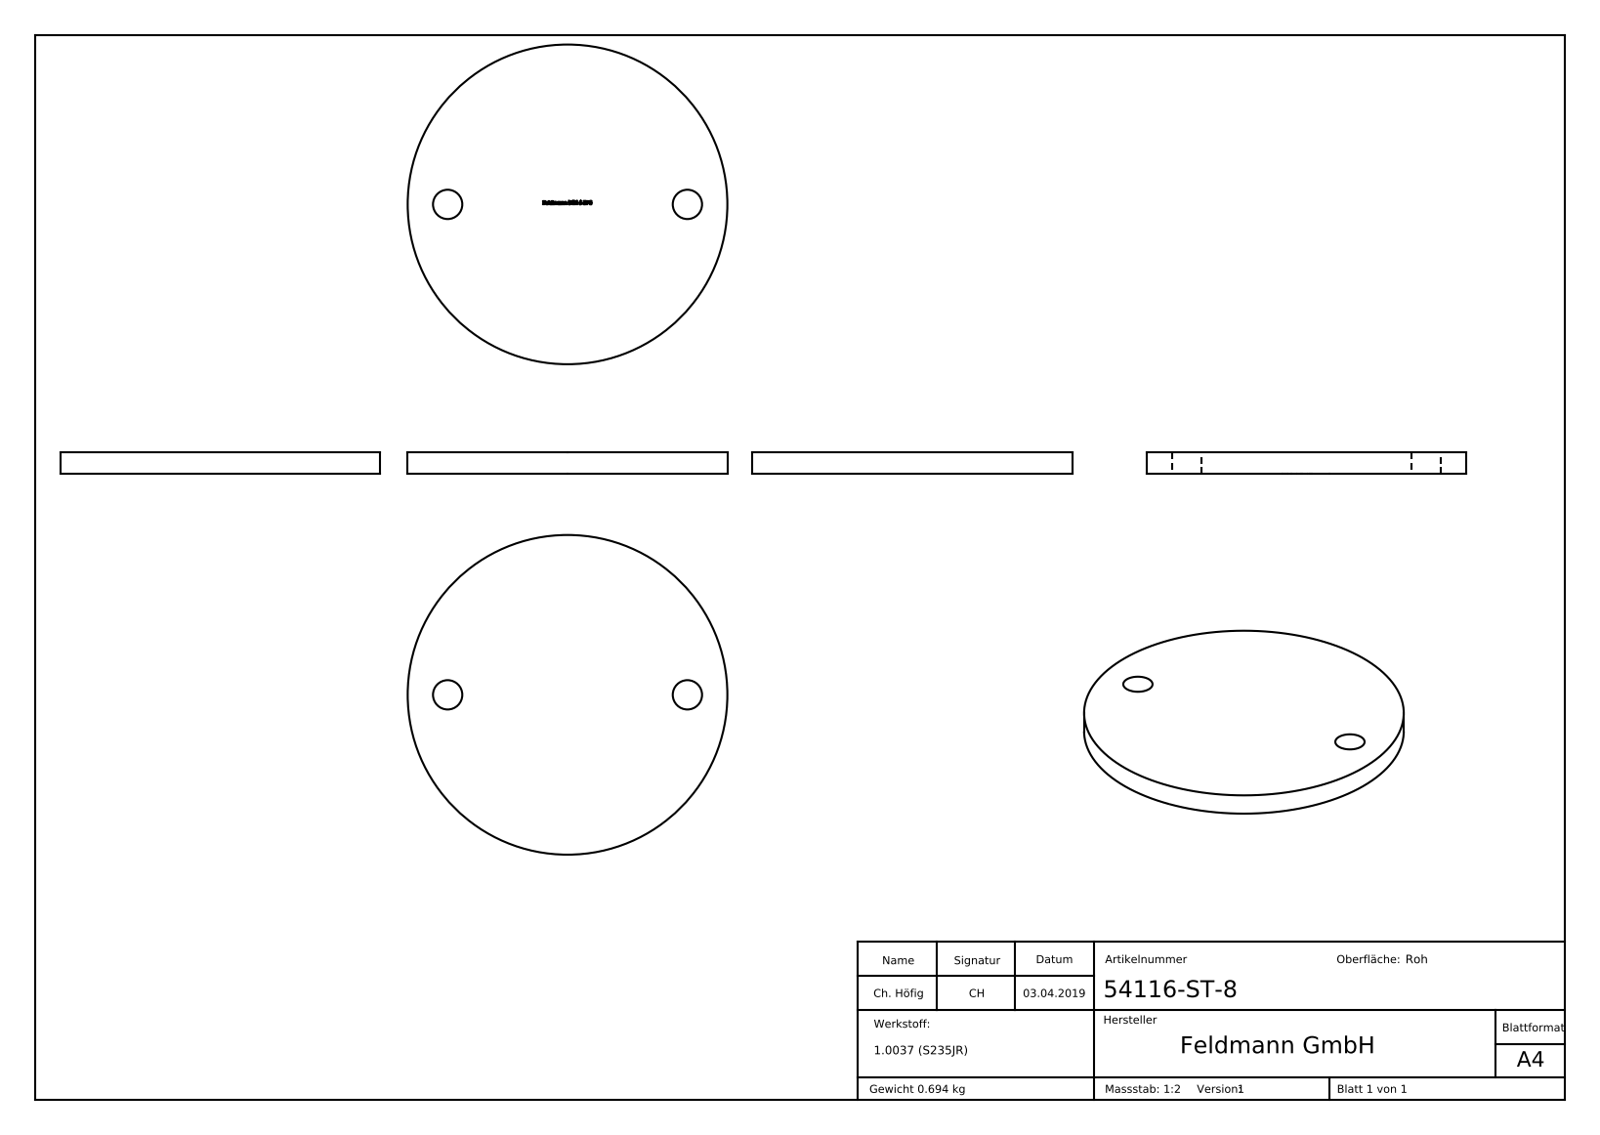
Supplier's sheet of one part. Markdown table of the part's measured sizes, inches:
| quantity | value |
| --- | --- |
| part name | 54116-ST-8 |
| STEP written by | SolidWorks 2015 (CONFIG_CONTROL_DESIGN) |
| units | inches |
| bodies | 1 solid, 236 faces (133 planar, 6 cylindrical, 97 other) |
| overall size | 4.724 × 4.724 × 0.315 |
| volume | 5.428 in³ |
| surface area | 40.02 in² |
| round holes (diameter × count) | 0.433 × 2 |
| round bosses / shafts (diameter × count) | 4.724 × 1 |
| main face-to-face distances | 0.315, 0.311, 0.206, 0.422, 0.035, 0.08, 0.557, 0.134, 0.052, 0.502 |
| hole center spacings | 3.543 |
